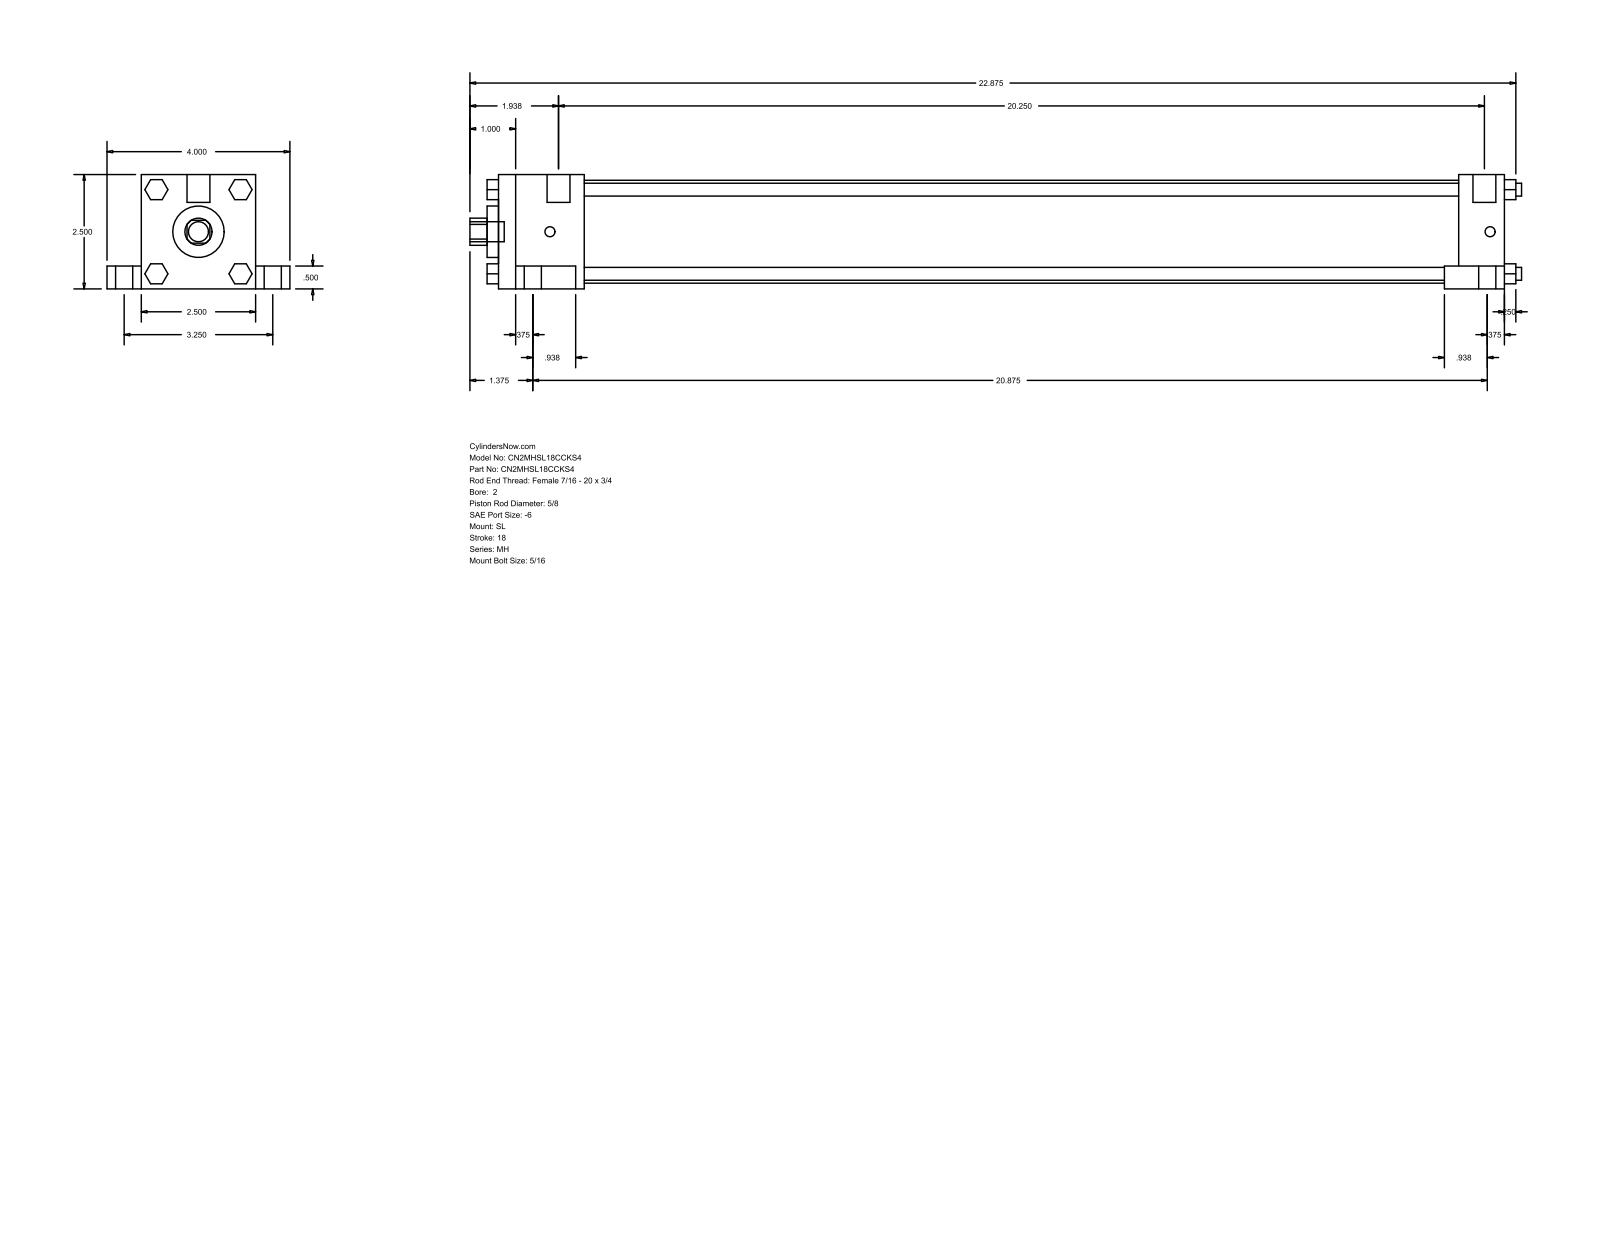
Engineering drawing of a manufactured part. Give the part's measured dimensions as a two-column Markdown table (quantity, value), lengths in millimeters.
| quantity | value |
| --- | --- |
| part name | MH_SL__0200_0.625 |
| STEP written by | GSSL Pune (CONFIG_CONTROL_DESIGN) |
| units | millimeters |
| bodies | 0 solids, 148 faces (112 planar, 36 cylindrical, 0 other) |
| overall size | 584.2 × 101.6 × 63.5 |
| round holes (diameter × count) | 15.88 × 1, 28.57 × 1, 57.15 × 1 |
| round bosses / shafts (diameter × count) | 15.88 × 4, 9.53 × 4, 7.14 × 4, 5.56 × 4, 12.7 × 2, 11.11 × 1 |
| partial cylindrical surfaces (radius × count) | 7.54 × 1 |
| main face-to-face distances | 63.5, 558.79, 12.7, 19.05, 50.8, 82.55, 25.4, 533.39, 47.62, 485.77 |
